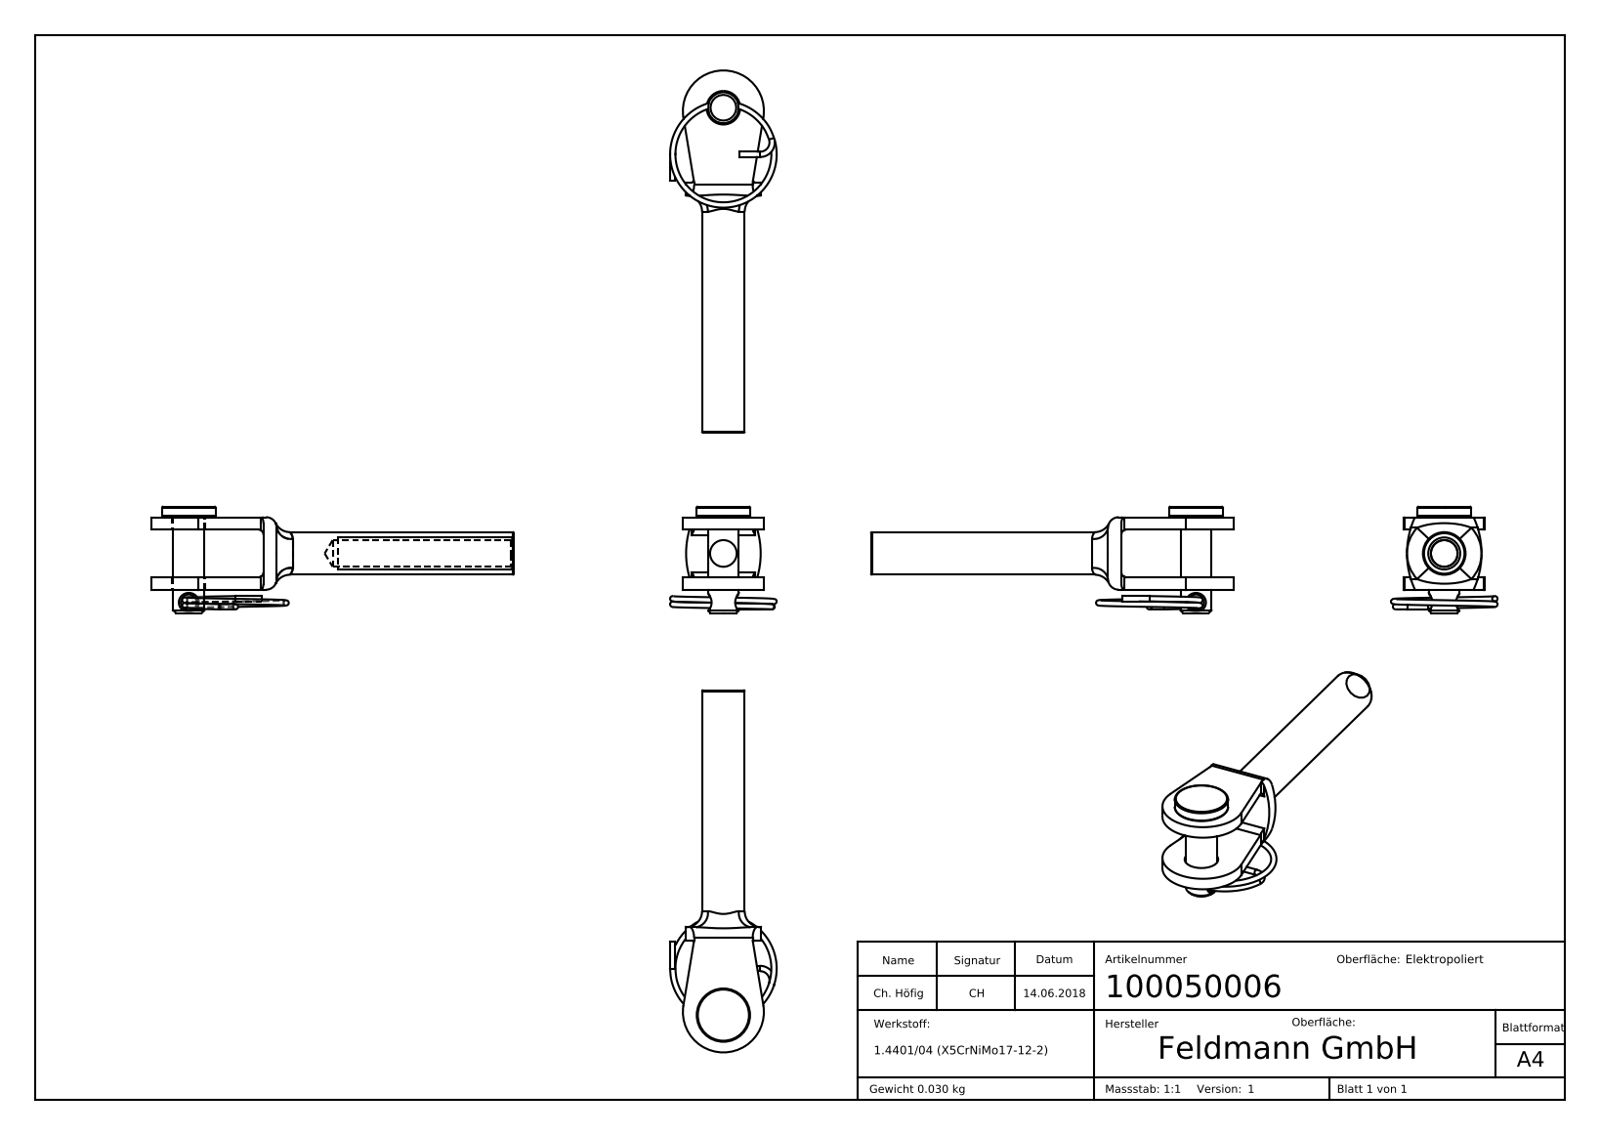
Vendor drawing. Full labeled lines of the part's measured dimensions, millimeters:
Part name (STEP PRODUCT): 10005000X Teil3_100050006 Teil2; 10005000X Teil2_100050006 Teil2; 100050006; 10005000X Teil1_100050006 Teil1
STEP written by: SolidWorks 2015 (CONFIG_CONTROL_DESIGN)
Units: millimetres
Bodies: 3 solids, 308 faces (88 planar, 76 cylindrical, 144 other)
Overall size (bounding box): 68 × 20 × 20
Volume: 3 788 mm³ · Surface area: 4 178 mm²
Round holes (diameter × count): ⌀3 ×1, ⌀5 ×1, ⌀6.3 ×1
Round bosses / shafts (diameter × count): ⌀1 ×2, ⌀10 ×1, ⌀8 ×1, ⌀5.8 ×1
Partial cylindrical surfaces — rounded edges, fillets, slot ends (radius × count): R0.4 ×2, R1 ×2, R2 ×2, R16.16 ×2, R2.6 ×1, R7.6 ×1
Main face-to-face distances: 2.3, 11.3, 13.6, 9, 2, 15.6, 13.3, 4.3, 4.4, 6.7
